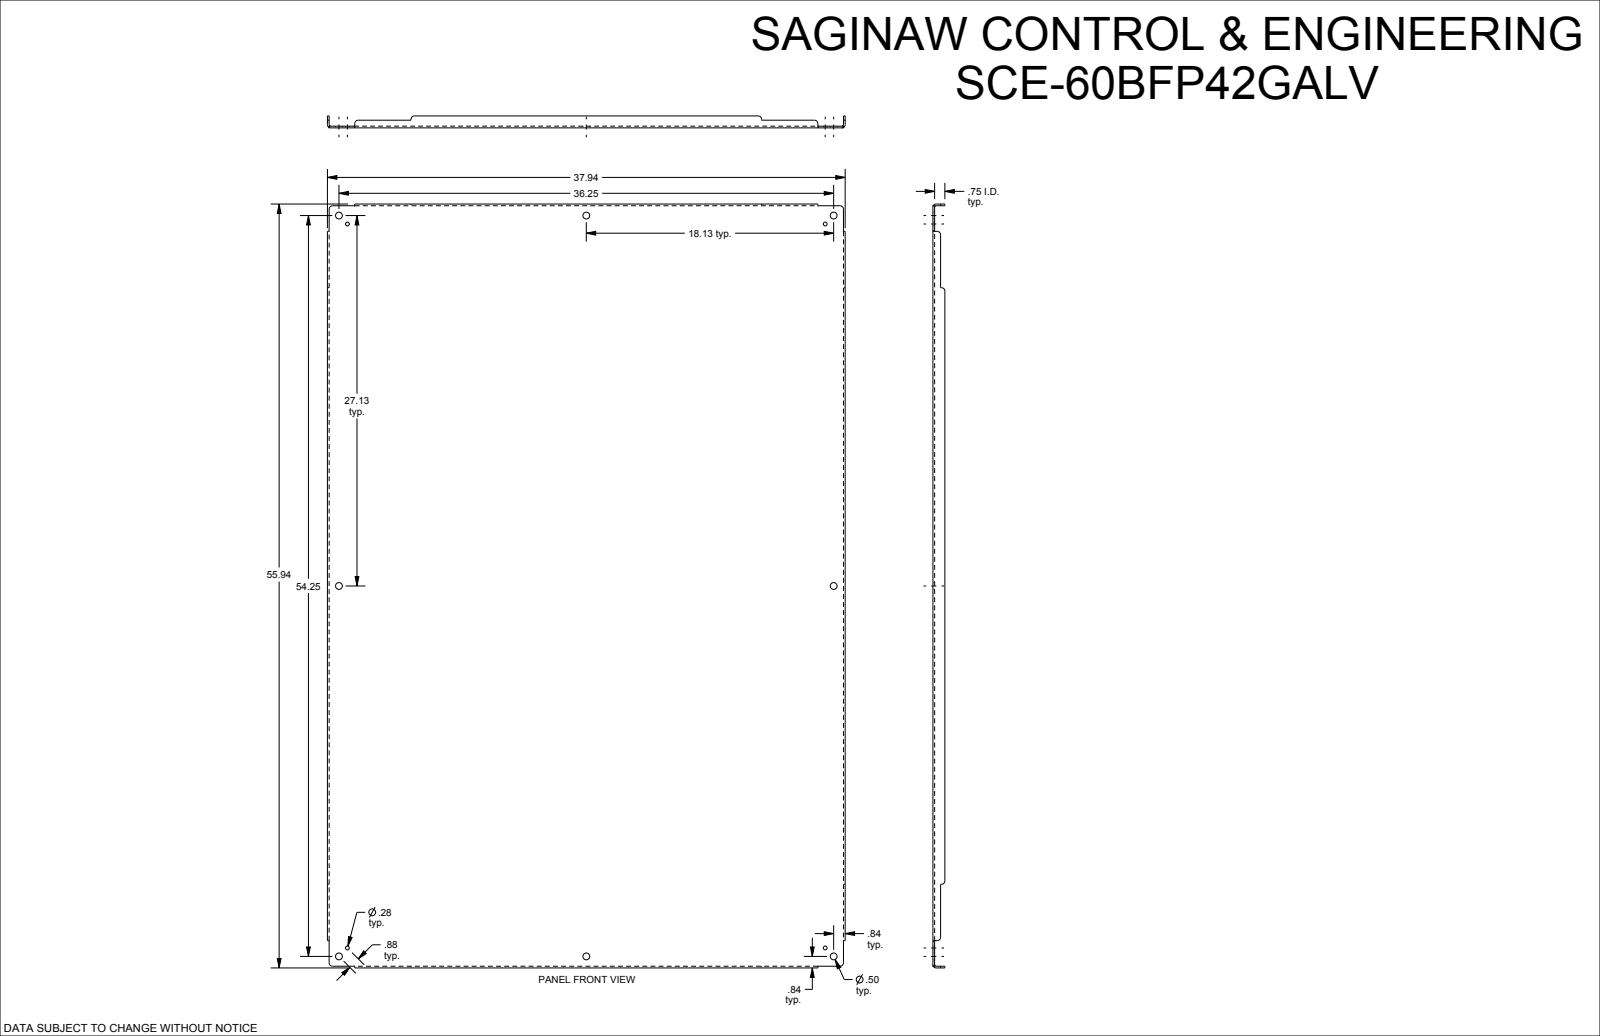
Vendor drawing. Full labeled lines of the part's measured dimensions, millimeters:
Part name (STEP PRODUCT): SCE-60BFP42GALV
STEP written by: SolidWorks 2019 (CONFIG_CONTROL_DESIGN)
Units: millimetres
Bodies: 1 solid, 110 faces (46 planar, 40 cylindrical, 24 other)
Overall size (bounding box): 1420.8 × 963.6 × 22.2
Volume: 4 556 000 mm³ · Surface area: 2 886 000 mm²
Round holes (diameter × count): ⌀12.7 ×8, ⌀7.1 ×4
Partial cylindrical surfaces — rounded edges, fillets, slot ends (radius × count): R6.4 ×12, R2.8 ×4, R6 ×4
Main face-to-face distances: 3.2, 3.2, 960.5, 1417.7, 957.2, 963.6, 1414.4, 1420.8, 19.1, 22.2
Hole centre spacings: 22.2, 444.9, 460.4, 673.4, 689, 828.6, 905.2, 1128
